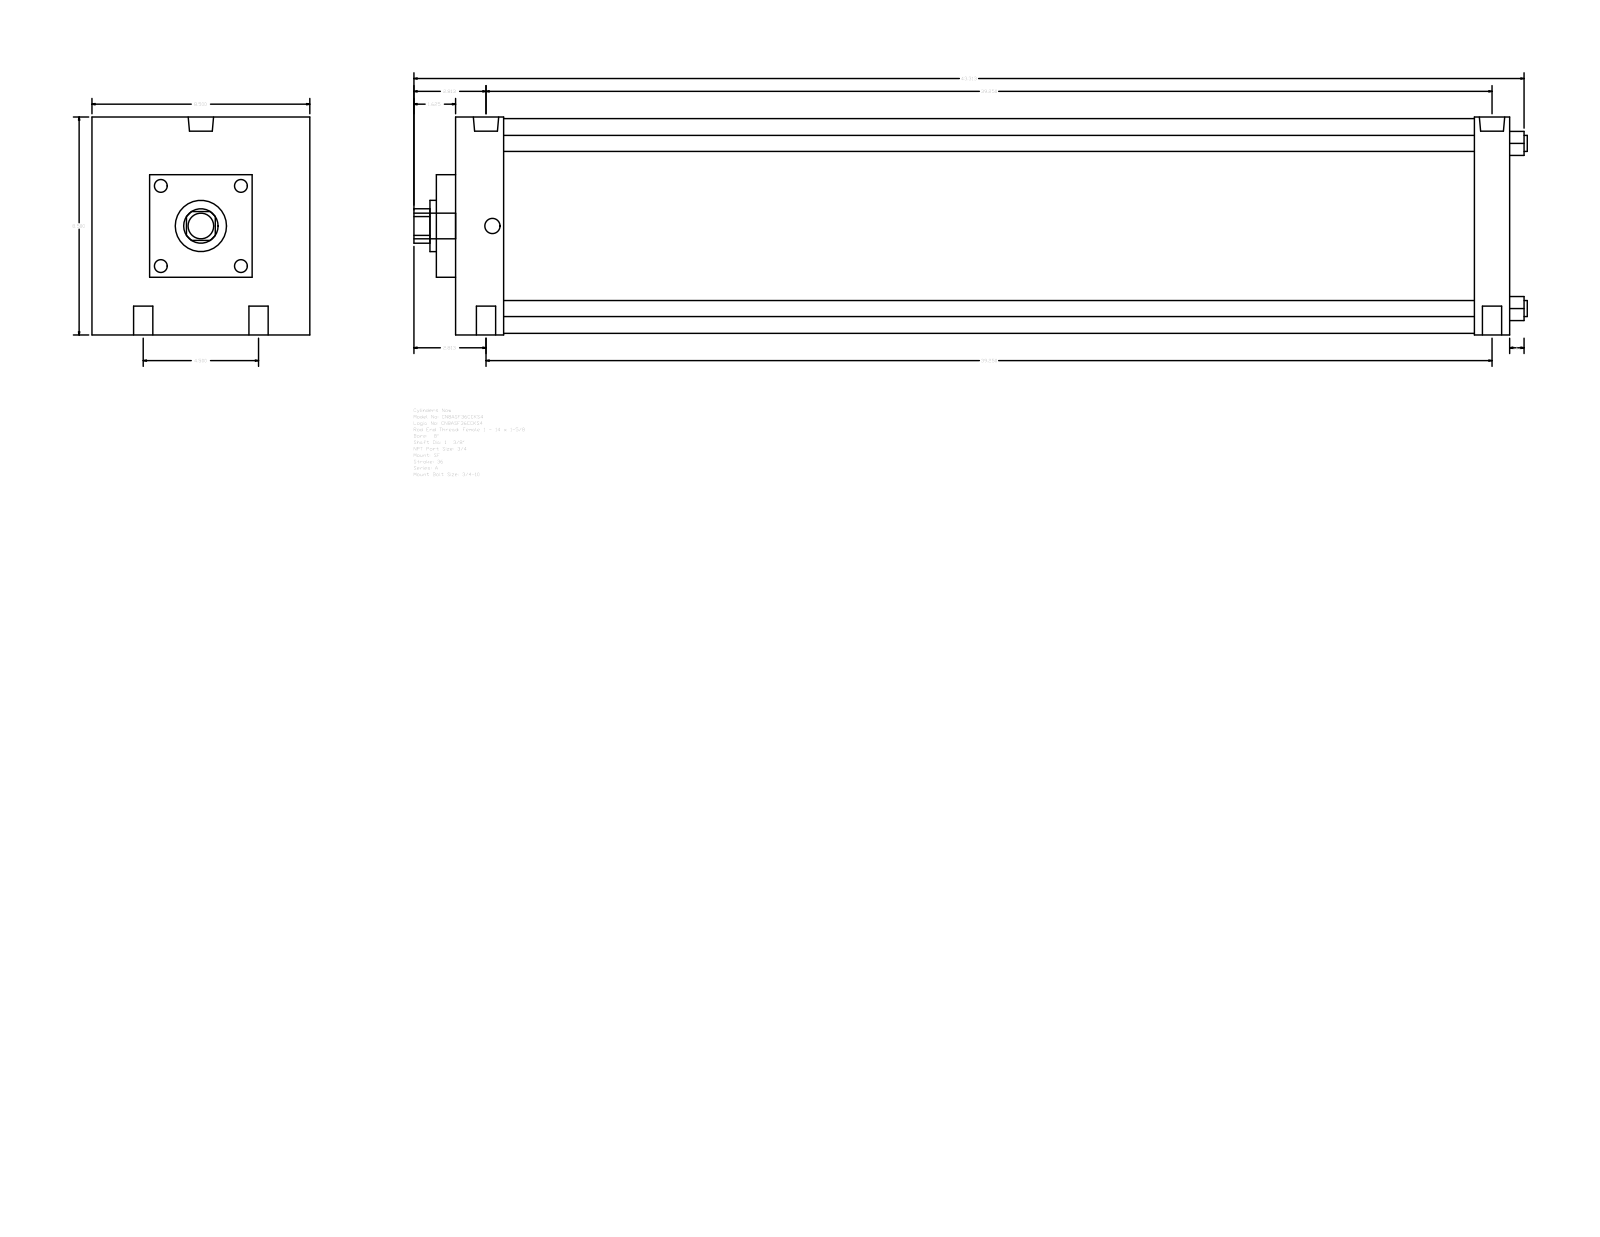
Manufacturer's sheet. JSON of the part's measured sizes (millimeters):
{"part_name": "A_SF__0800_1.375", "step_written_by": "GSSL Pune (CONFIG_CONTROL_DESIGN)", "units": "millimeters", "bodies": {"solids": 0, "faces": 93, "planar": 67, "cylindrical": 26, "other": 0}, "overall_size": [1103.31, 215.9, 215.9], "round_holes": [[19.05, 4], [15.08, 2], [25.12, 2], [34.92, 1], [50.8, 1]], "round_bosses_or_shafts": [[15.88, 4], [212.72, 1], [25.4, 1]], "partial_cylinders_radius": [[17.06, 1]], "face_to_face_distances": [1044.58, 215.9, 47.63, 1009.65, 962.02, 996.95, 34.93, 19.04, 66.67, 1028.69], "hole_center_spacings": [57.15, 998.59, 996.95, 114.3, 1003.48, 984.25]}
